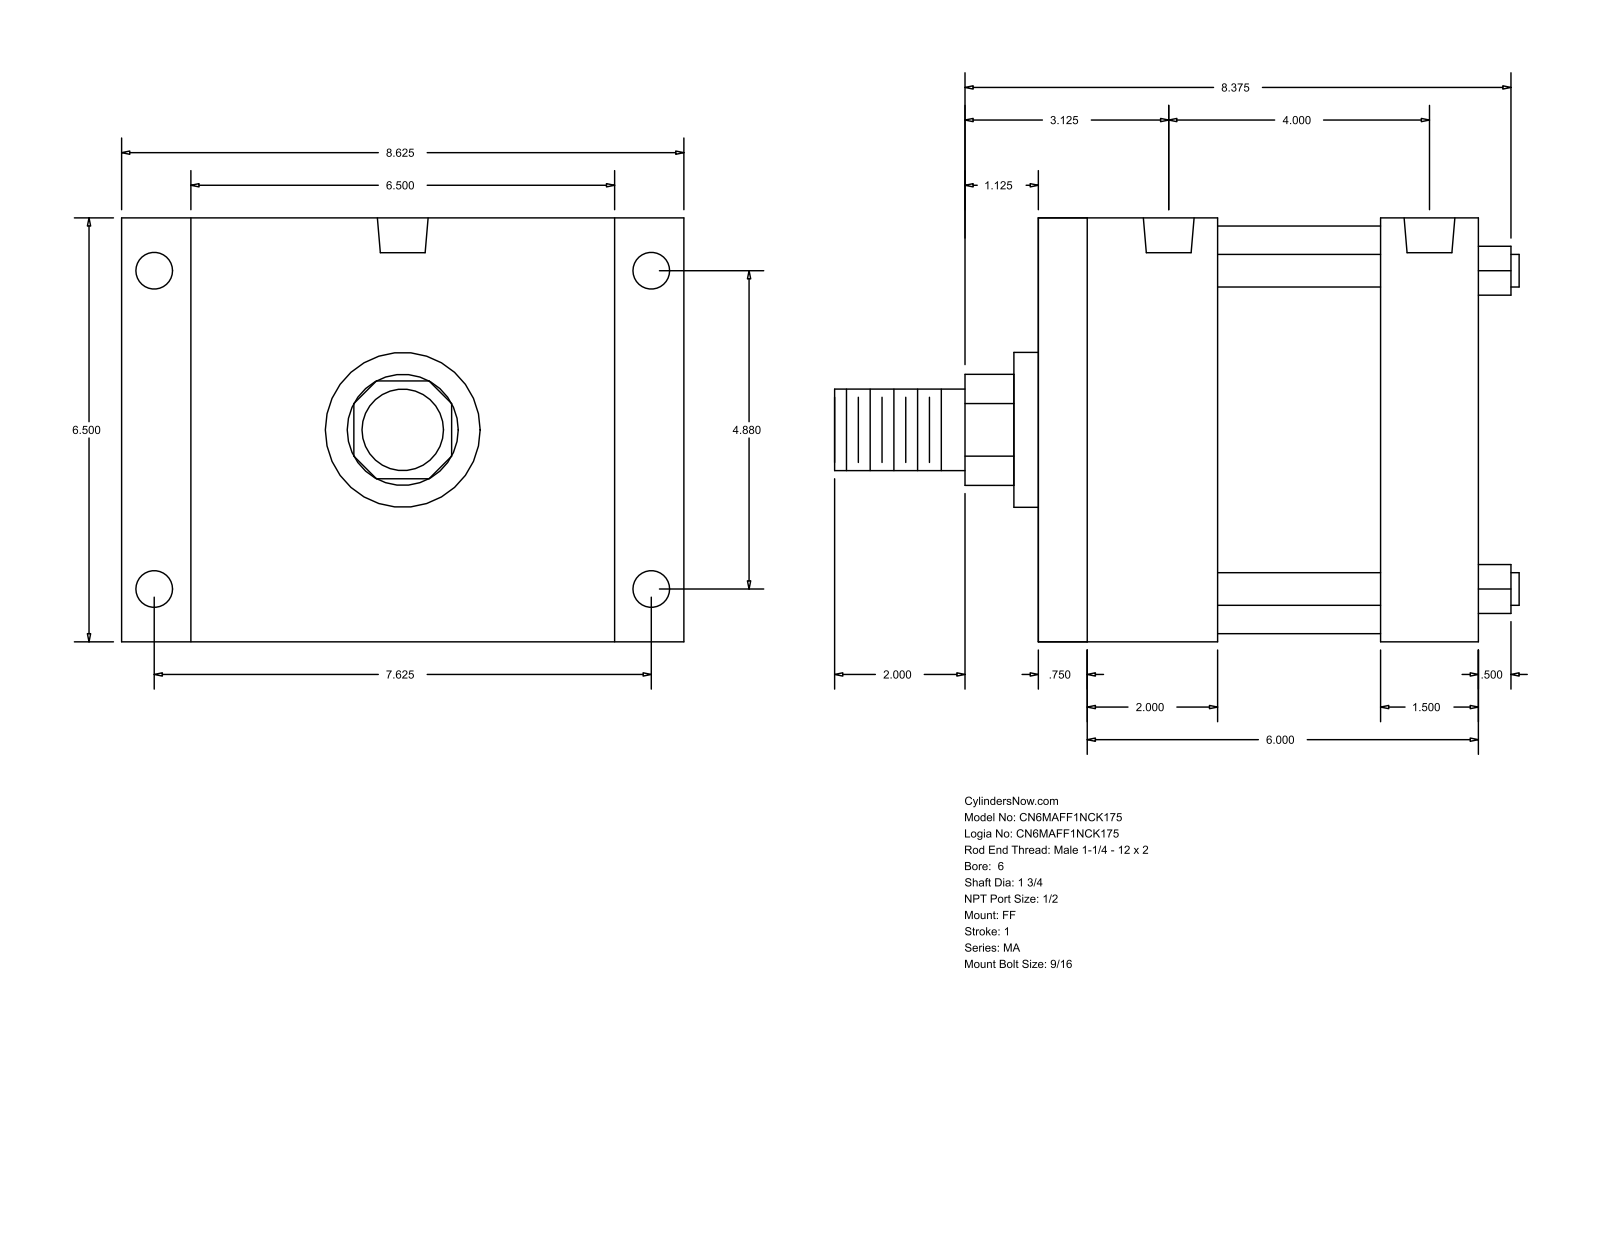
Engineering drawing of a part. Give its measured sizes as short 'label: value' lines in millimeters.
name: MA_FF__0600_1.75
written by: GSSL Pune (CONFIG_CONTROL_DESIGN)
unit: mm
bodies: 0 solids, 92 faces (64 planar, 28 cylindrical, 0 other)
size: 266.7 × 219.07 × 165.1
holes: 4× ⌀14.29, 4× ⌀17.46, 2× ⌀19.77
bosses: 4× ⌀12.7, 1× ⌀158.75, 1× ⌀60.33, 1× ⌀44.45, 1× ⌀31.75
rounds: 1× R21.63
face distances: 165.1, 171.46, 19.05, 152.41, 69.85, 38.1, 50.8, 101.61, 133.36, 114.31
hole spacings: 101.59, 123.96, 193.68, 229.95
